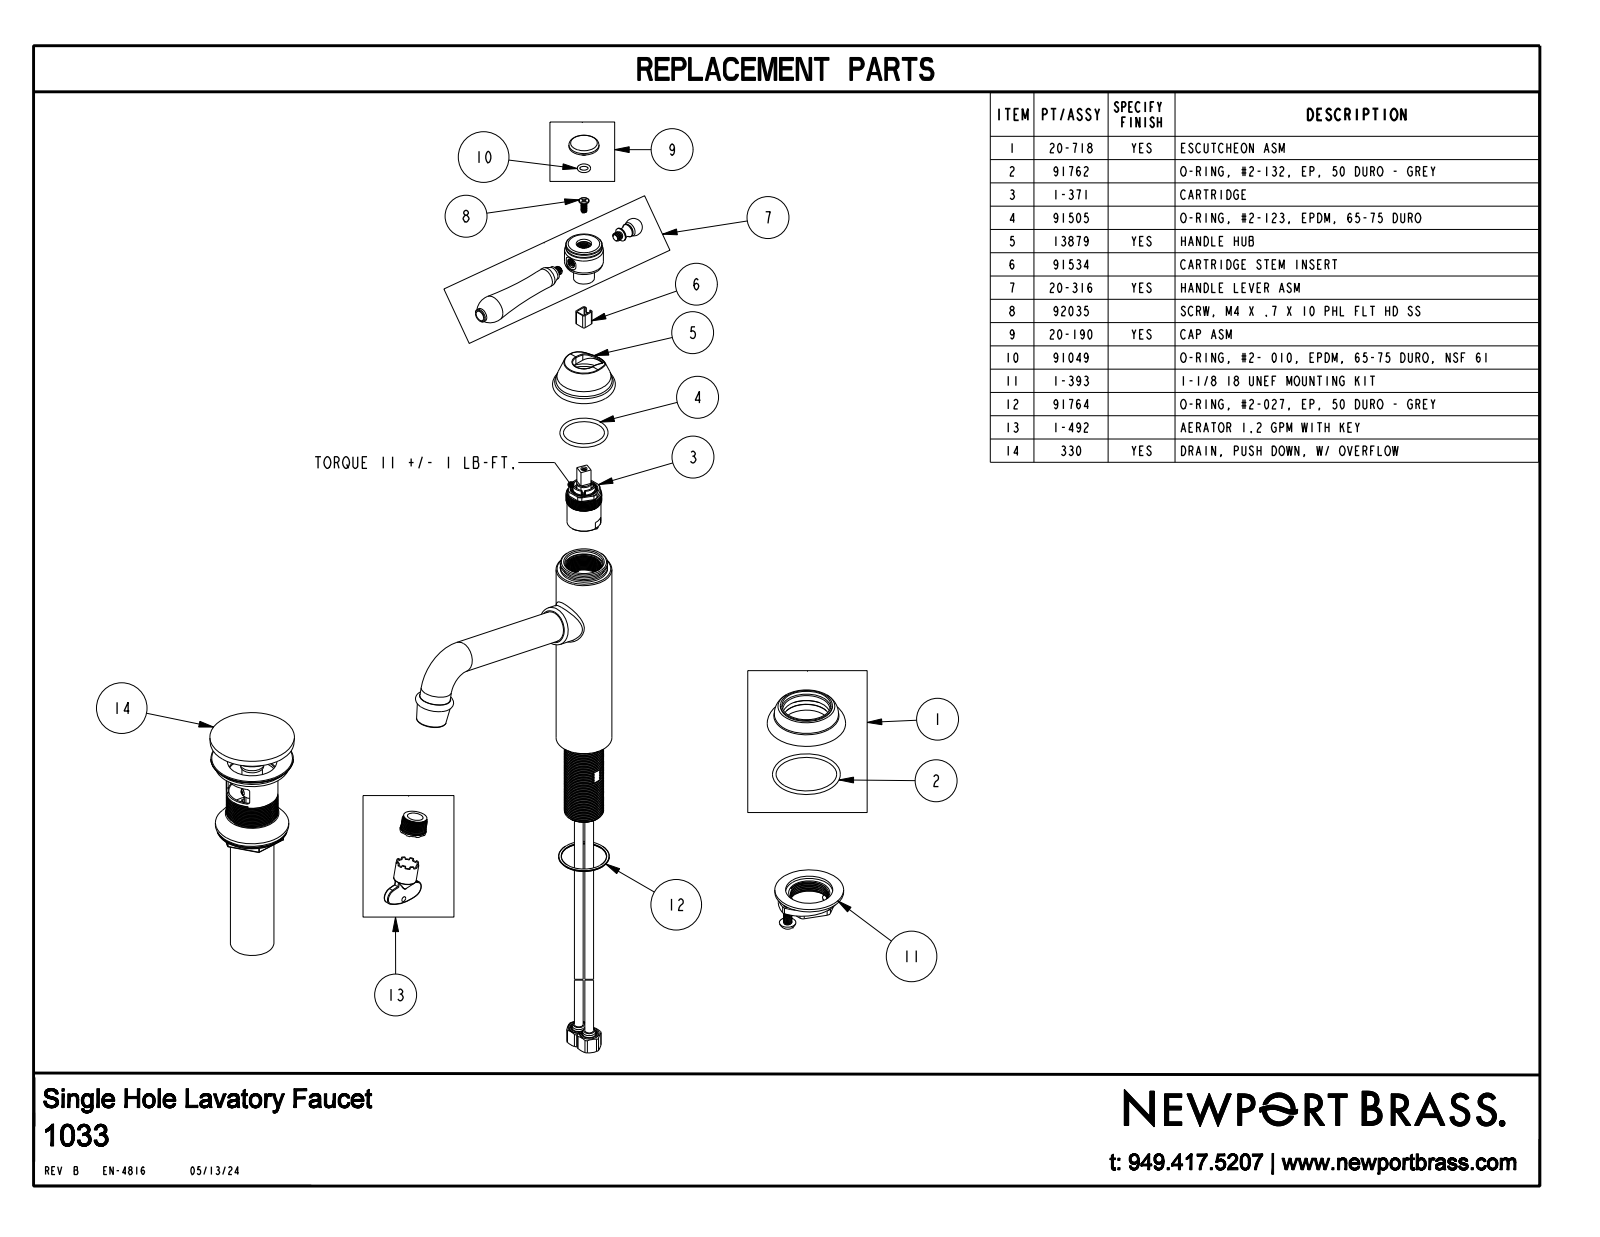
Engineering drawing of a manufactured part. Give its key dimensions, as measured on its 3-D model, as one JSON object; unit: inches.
{"part_name": "1033_SW0001", "step_written_by": "CREO PARAMETRIC BY PTC INC, 2023134 (CONFIG_CONTROL_DESIGN)", "units": "inches", "bodies": {"solids": 1, "faces": 126, "planar": 17, "cylindrical": 33, "other": 76}, "overall_size": [8.528, 7.901, 2.245], "volume_in3": 21.11, "surface_area_in2": 74.59, "round_holes": [[1.65, 1]], "round_bosses_or_shafts": [[0.875, 2], [1.6, 1], [1.11, 1], [1.1, 1], [1.048, 1], [0.86, 1], [0.6, 1], [0.563, 1]], "partial_cylinders_radius": [[0.02, 2], [0.325, 2], [0.196, 1], [0.5, 1], [1, 1]], "face_to_face_distances": [7.33, 7.089, 0.24, 7.588, 0.499, 0.259, 6.465, 0.624, 0.864, 1.123]}
